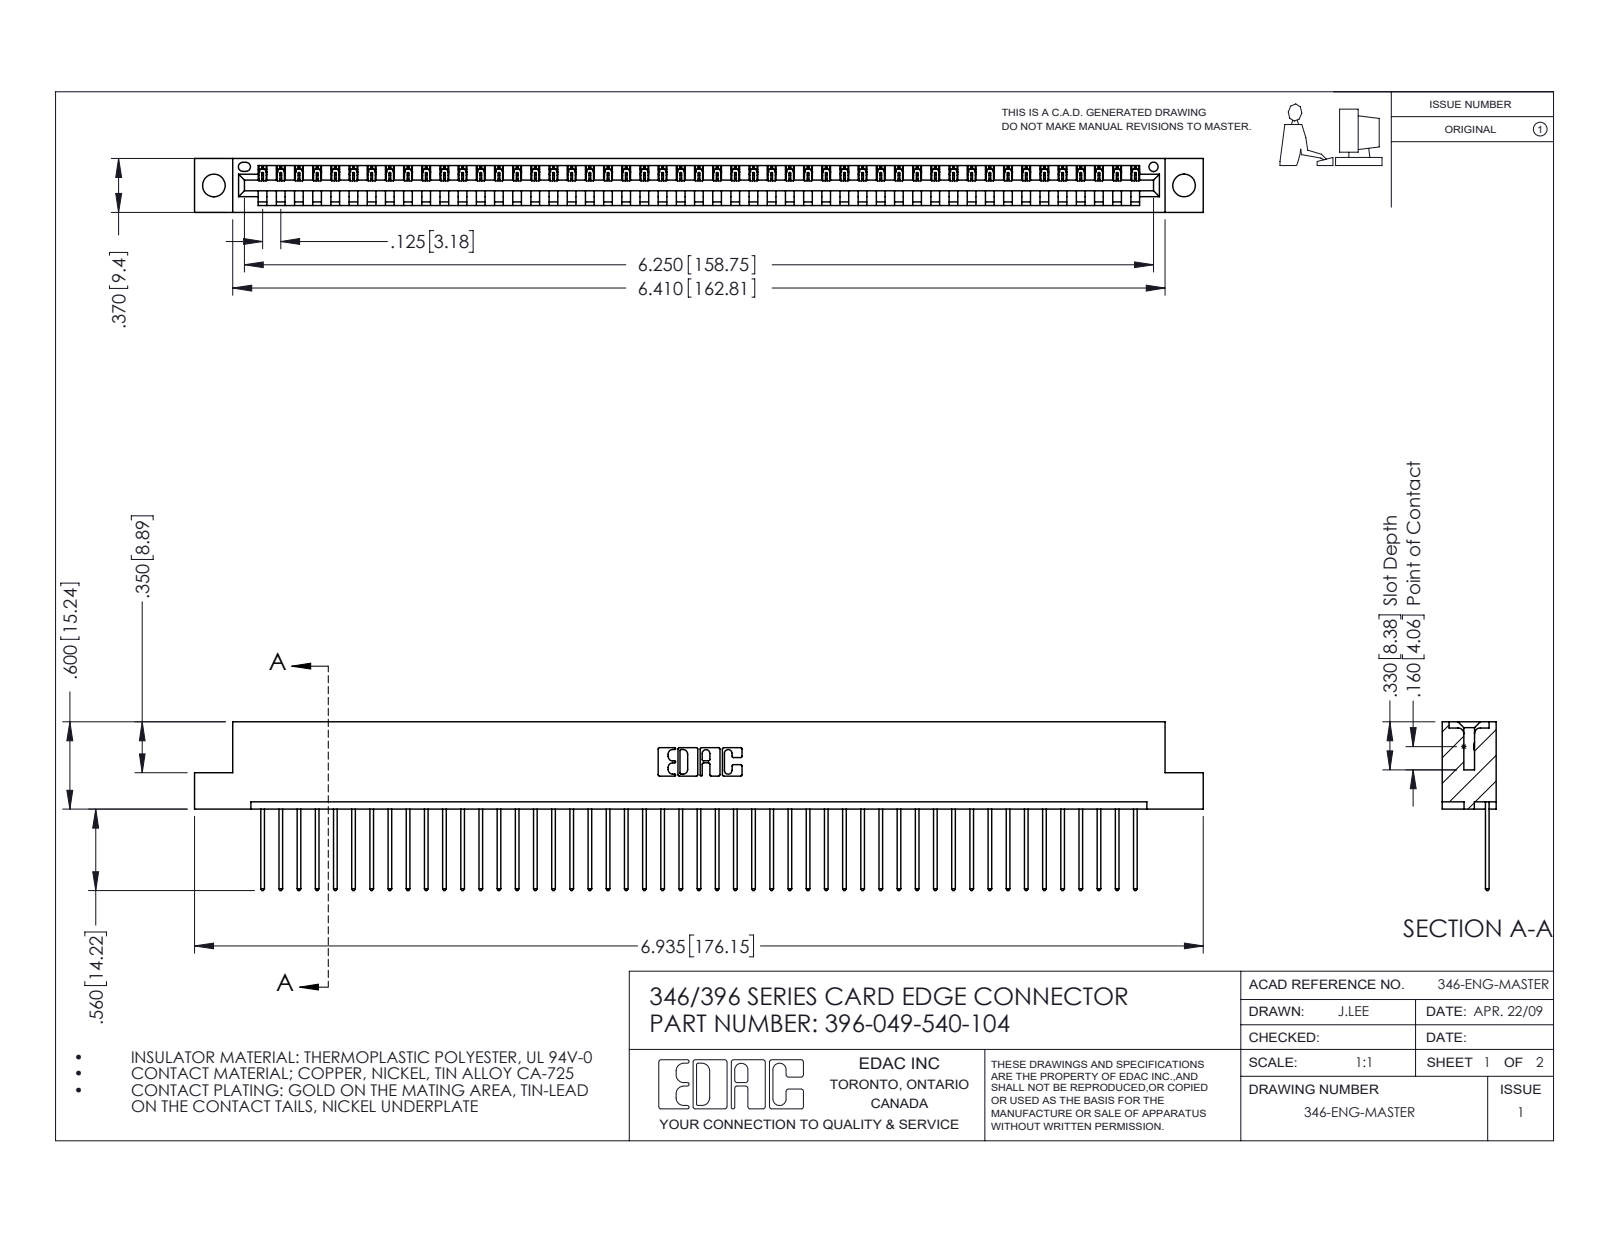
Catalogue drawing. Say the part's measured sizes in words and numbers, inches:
The part is named "396-049-540-104; 346 Part_Flush Mounting Lugs - 0.156 Dia-TH; 345-292-001_345-293-140". Its 3-D file was written by "SolidWorks 2016 (CONFIG_CONTROL_DESIGN)". It is 50 solids with 2964 faces: 2036 planar, 928 cylindrical and 0 other. Overall it measures 6.935 by 1.16 by 0.37 inches. Its volume is 1.031 cubic inches and its surface area 33.28 square inches. Round holes: 2 of diameter 0.156, 1 of diameter 0.064. Partial cylindrical surfaces (rounded edges, fillets, slot ends): 98 of radius 0.006, 98 of radius 0.01, 22 of radius 0.01, 6 of radius 0.007, 6 of radius 0.031, 3 of radius 0.026, 2 of radius 0.031, 2 of radius 0.04. The main face-to-face distances are 0.048, 0.322, 0.37, 0.25, 0.072, 0.298, 0.025, 0.148, 0.222, 0.1. The hole center spacings are 0.246, 6.461, 6.67.
